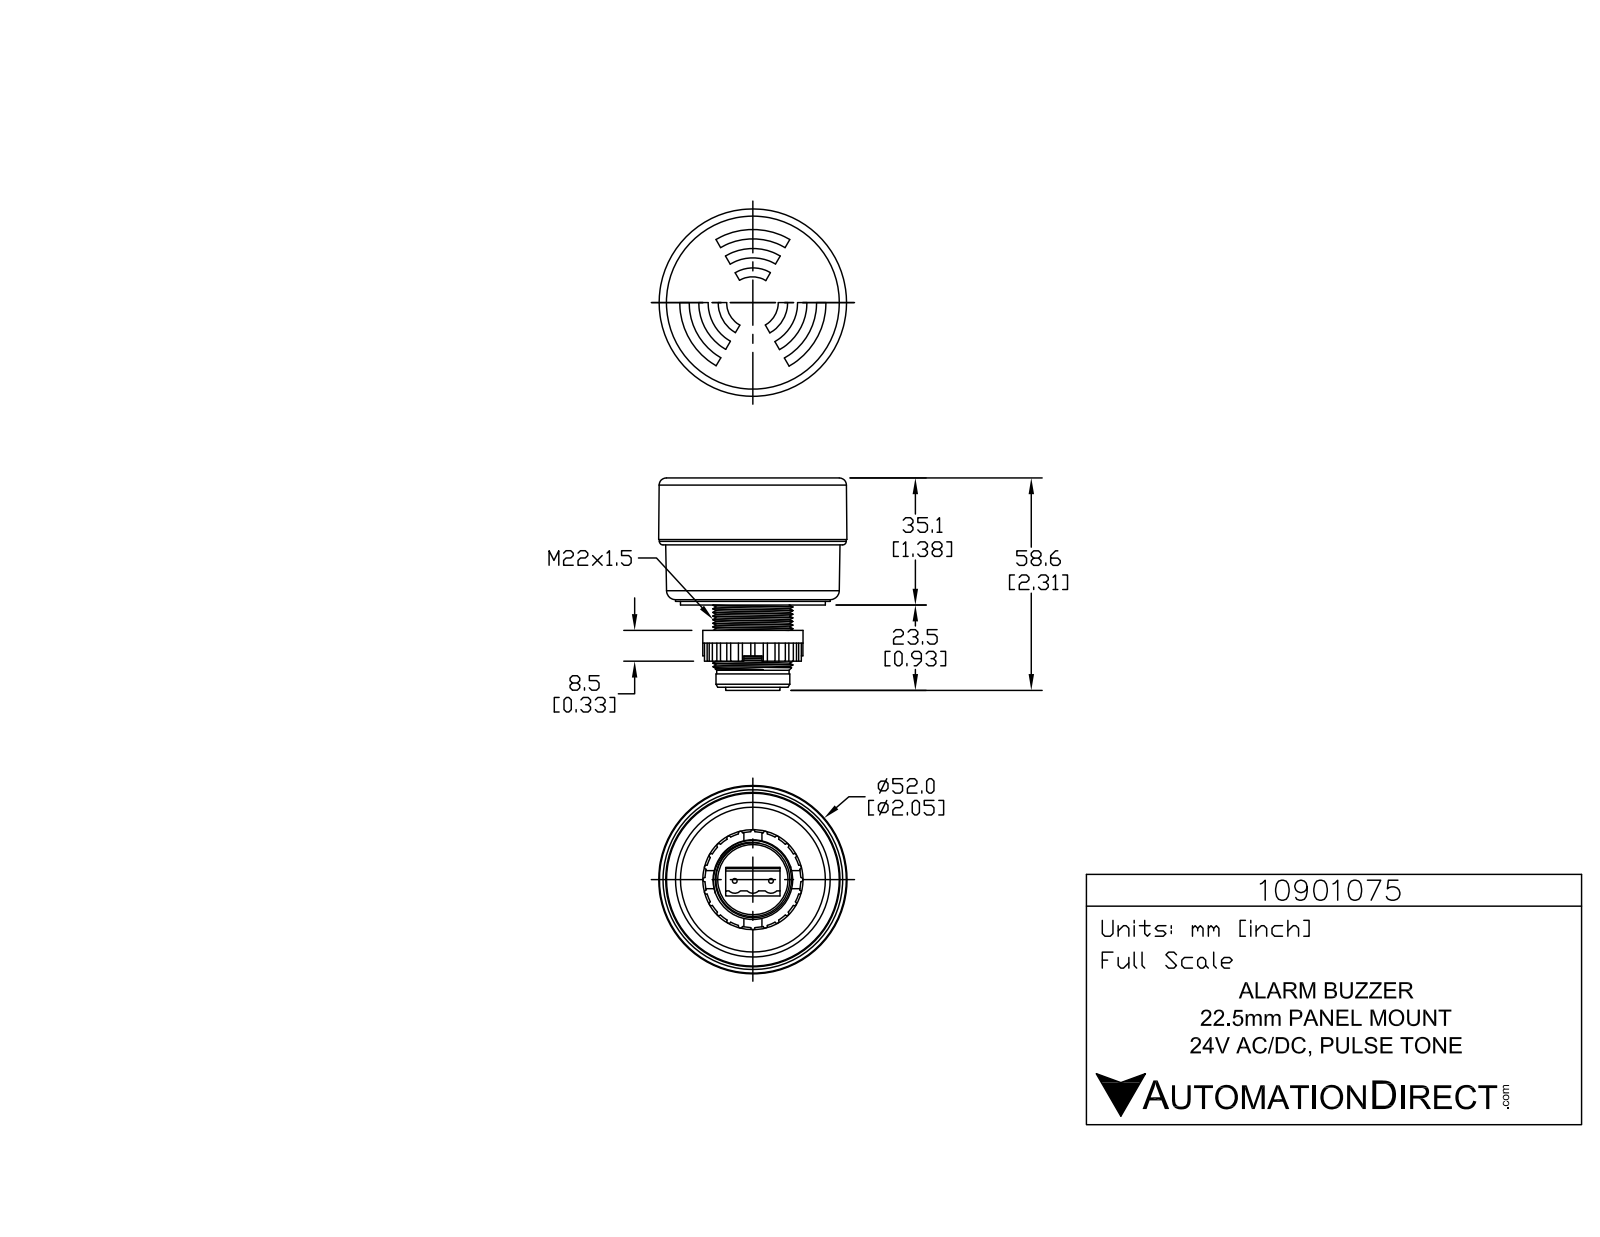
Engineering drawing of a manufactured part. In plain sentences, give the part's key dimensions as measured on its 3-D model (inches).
The part is named "10901075". Its 3-D file was written by "SolidWorks 2017 (AUTOMOTIVE_DESIGN)". It is 1 solid with 1180 faces: 766 planar, 311 cylindrical and 103 other. Overall it measures 2.309 by 2.054 by 2.05 inches. Its volume is 4.656 cubic inches and its surface area 22.8 square inches. Round holes: 4 of diameter 0.039, 1 of diameter 0.906. Round bosses or shafts: 4 of diameter 0.226, 4 of diameter 0.056, 2 of diameter 0.051, 1 of diameter 2.031, 1 of diameter 1.681, 1 of diameter 1.575, 1 of diameter 1.091, 1 of diameter 0.866. Partial cylindrical surfaces (rounded edges, fillets, slot ends): 24 of radius 0.023, 8 of radius 0.008, 8 of radius 0.008, 8 of radius 0.008, 8 of radius 0.131, 4 of radius 0.004, 4 of radius 0.005, 4 of radius 0.008. The main face-to-face distances are 1.374, 0.276, 1.65, 0.039, 0.315, 1.335, 0.898, 0.937, 0.622, 2.272. The hole center spacings are 0.242.
